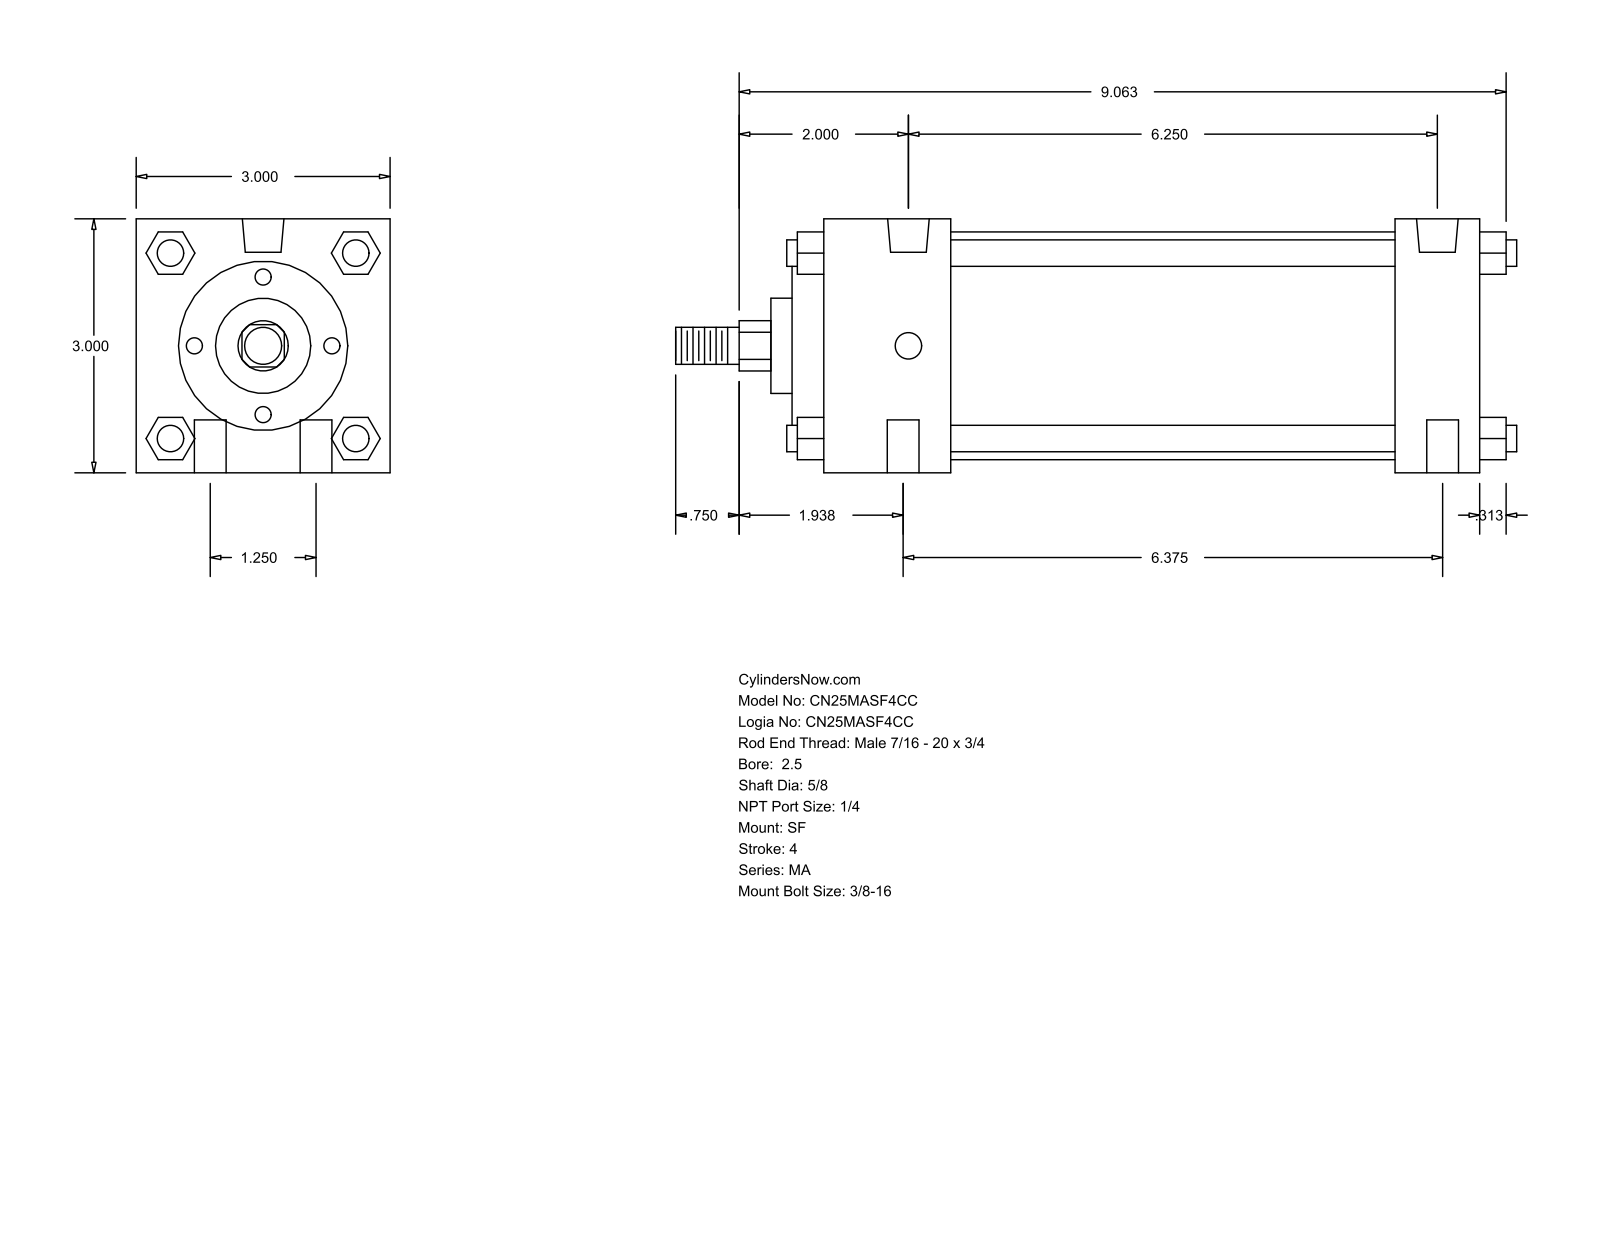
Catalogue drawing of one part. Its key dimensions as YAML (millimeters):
part_name: "MA_SF__0250_0.625"
step_written_by: "GSSL Pune (CONFIG_CONTROL_DESIGN)"
units: millimeters
bodies: {solids: 0, faces: 126, planar: 95, cylindrical: 31, other: 0}
overall_size: [252.41, 76.2, 76.2]
round_holes:
  - {diameter: 9.53, count: 4}
  - {diameter: 7.94, count: 2}
  - {diameter: 12.49, count: 2}
round_bosses_or_shafts:
  - {diameter: 7.94, count: 4}
  - {diameter: 68.33, count: 1}
  - {diameter: 50.8, count: 1}
  - {diameter: 28.57, count: 1}
  - {diameter: 15.88, count: 1}
  - {diameter: 11.11, count: 1}
partial_cylinders:
  - {radius: 7.54, count: 1}
face_to_face_distances: [76.2, 196.85, 25.4, 171.45, 38.1, 133.35, 158.75, 12.7, 9.52, 47.62]
hole_center_spacings: [15.96, 161.12, 31.76, 158.75, 161.93, 165.02]
